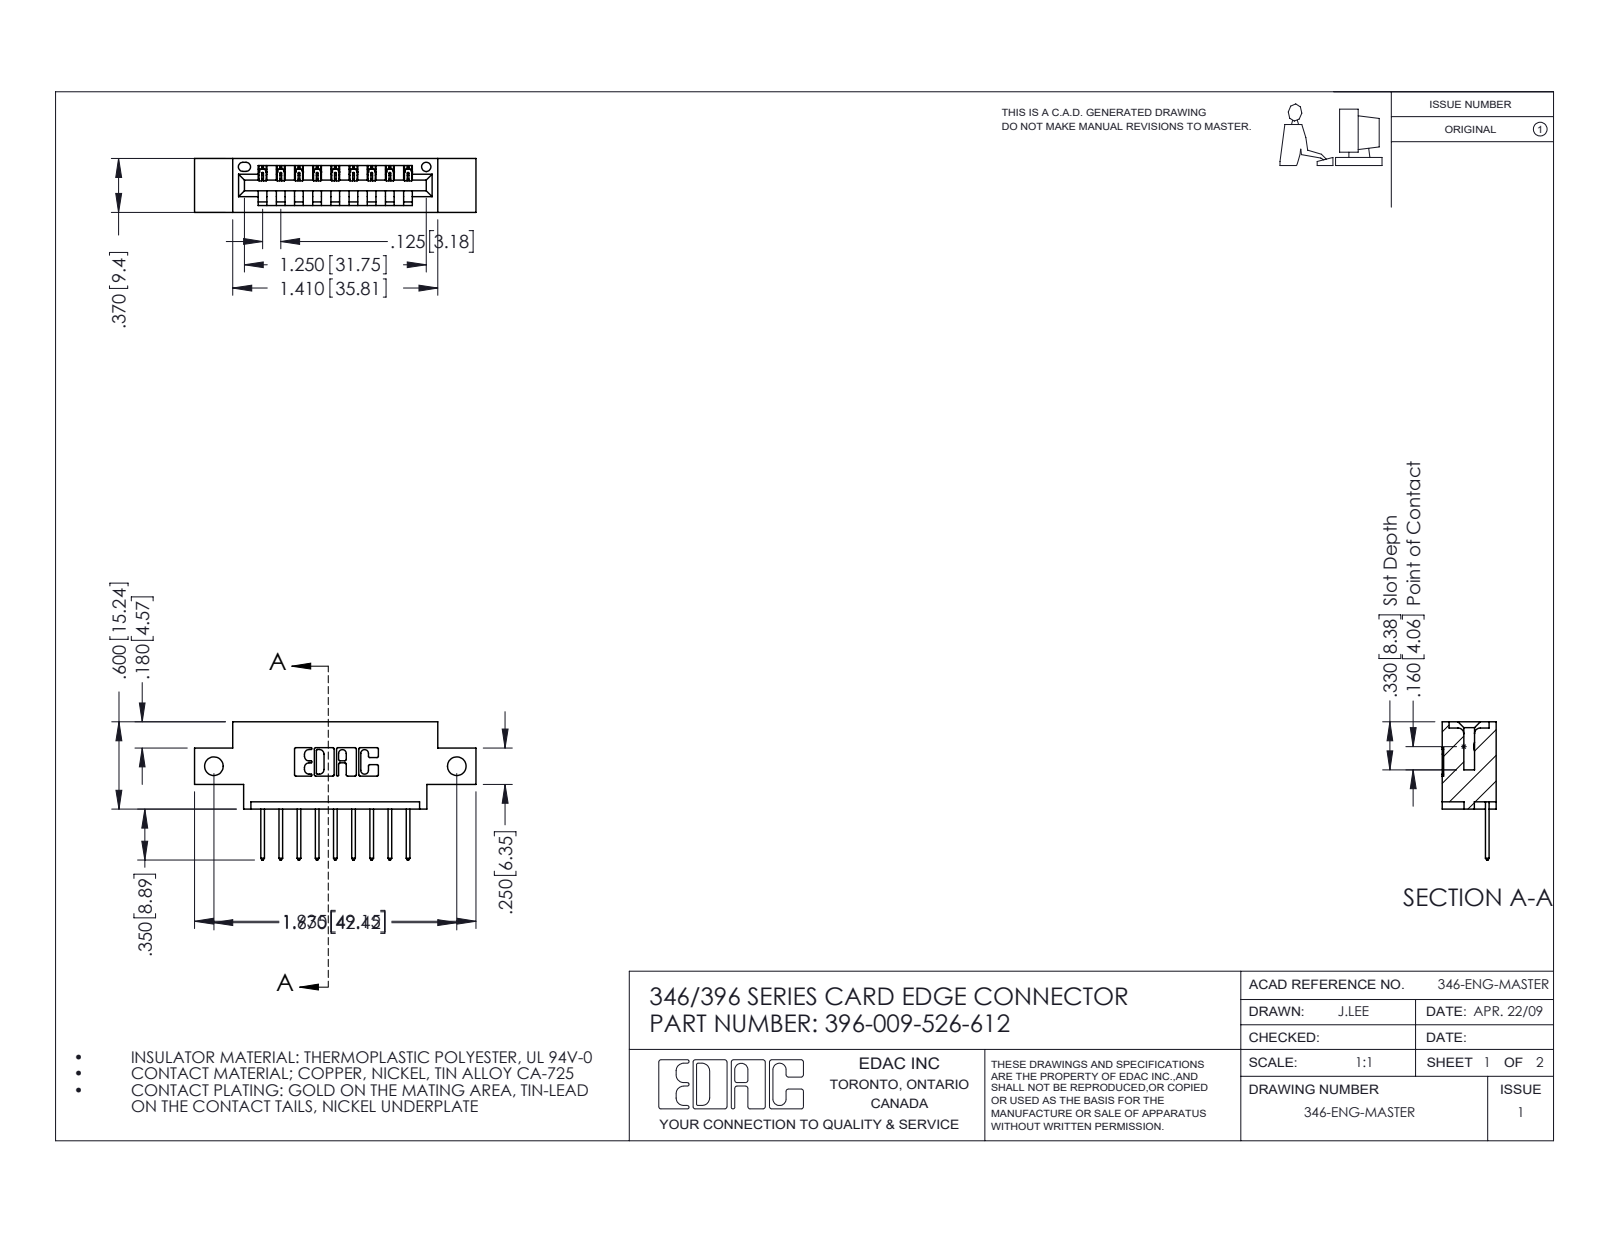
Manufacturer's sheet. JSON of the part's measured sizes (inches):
{"part_name": "345-292-001_345-293-126; 396-009-526-612; 346 Part_0.170 Offset - Side Mount", "step_written_by": "SolidWorks 2016 (CONFIG_CONTROL_DESIGN)", "units": "inches", "bodies": {"solids": 10, "faces": 648, "planar": 440, "cylindrical": 208, "other": 0}, "overall_size": [1.935, 0.95, 0.37], "volume_in3": 0.258, "surface_area_in2": 7.648, "round_holes": [[0.128, 2], [0.064, 1]], "partial_cylinders_radius": [[0.01, 22], [0.006, 18], [0.01, 18], [0.007, 6], [0.031, 6], [0.026, 3], [0.031, 2], [0.04, 2]], "face_to_face_distances": [0.25, 0.37, 0.048, 0.322, 0.072, 0.298, 0.025, 0.148, 0.222, 0.1], "hole_center_spacings": [1.67]}
